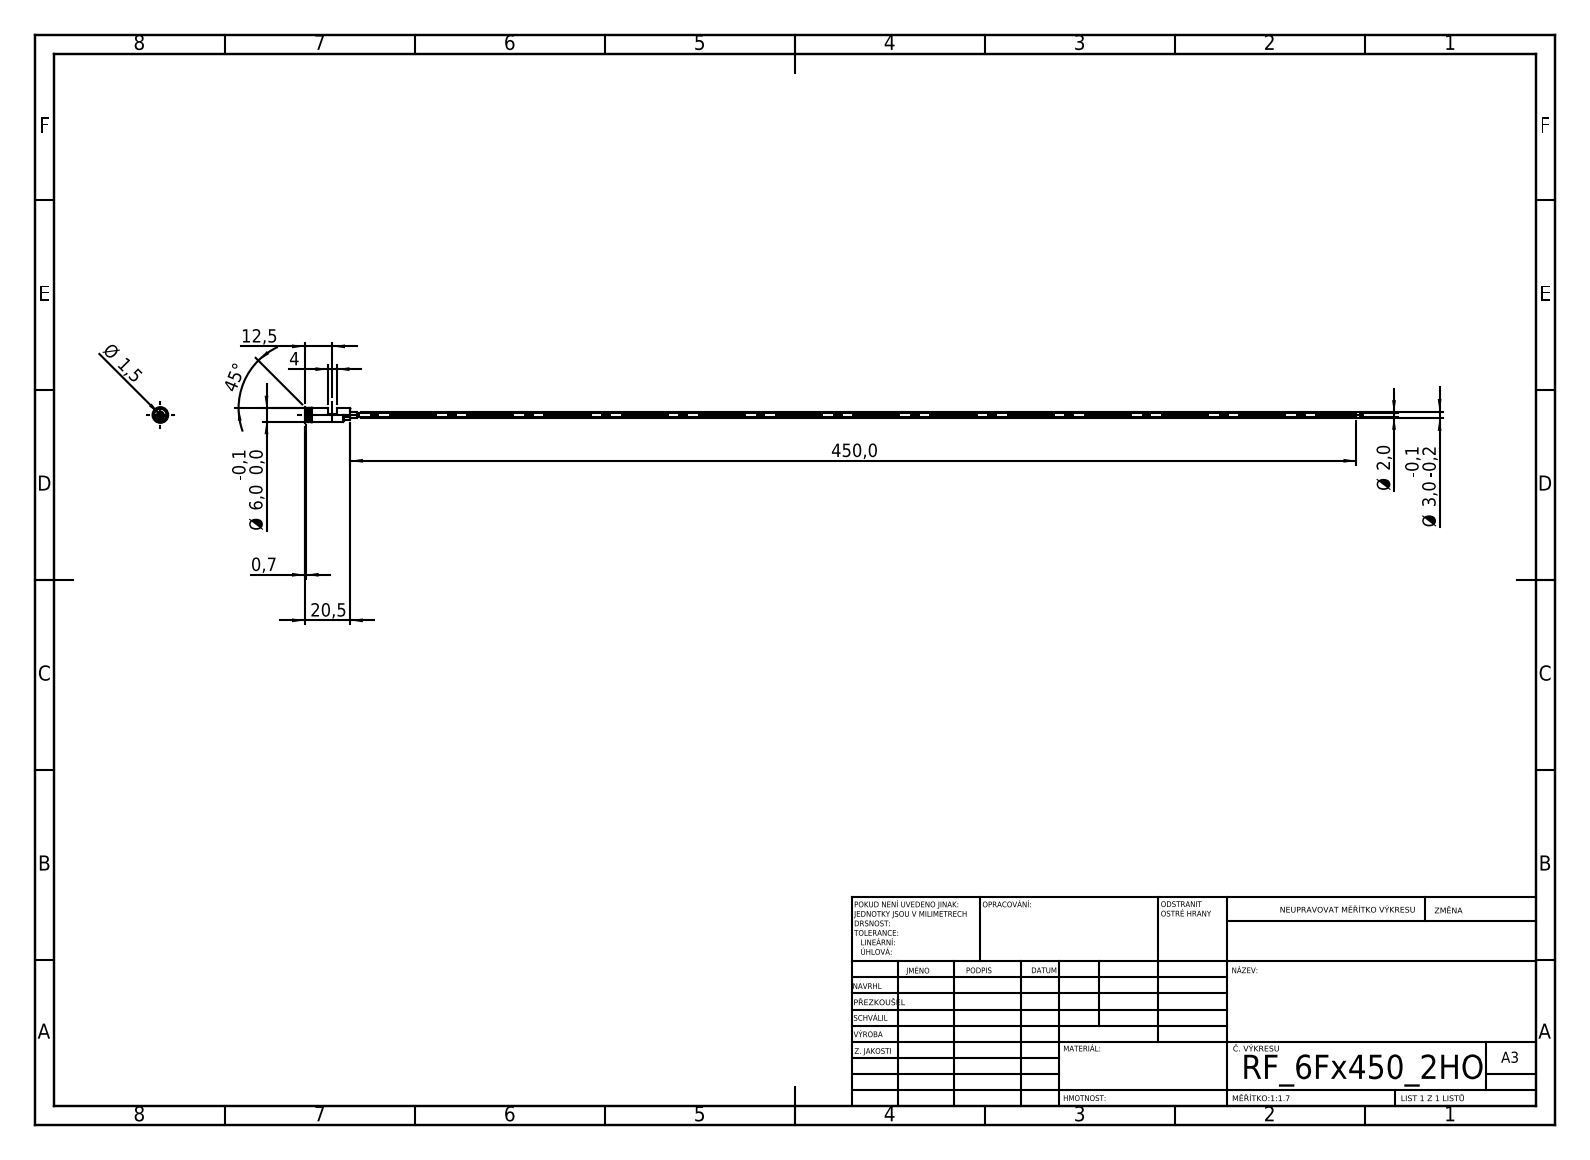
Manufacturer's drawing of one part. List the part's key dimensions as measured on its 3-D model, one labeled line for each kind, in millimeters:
STEP written by: SolidWorks 2019 (CONFIG_CONTROL_DESIGN)
Units: millimetres
Bodies: 1 solid, 55 faces (24 planar, 19 cylindrical, 12 other)
Overall size (bounding box): 470.5 × 7 × 7
Volume: 1 129 mm³ · Surface area: 5 483 mm²
Round holes (diameter × count): ⌀1.5 ×1
Round bosses / shafts (diameter × count): ⌀7 ×1, ⌀6 ×1, ⌀5.8 ×1, ⌀3 ×1, ⌀2 ×1
Partial cylindrical surfaces — rounded edges, fillets, slot ends (radius × count): R3 ×2, R2.05 ×1
Main face-to-face distances: 3, 6, 20.5, 10, 10.5, 14.5, 4, 2, 7, 17.5
